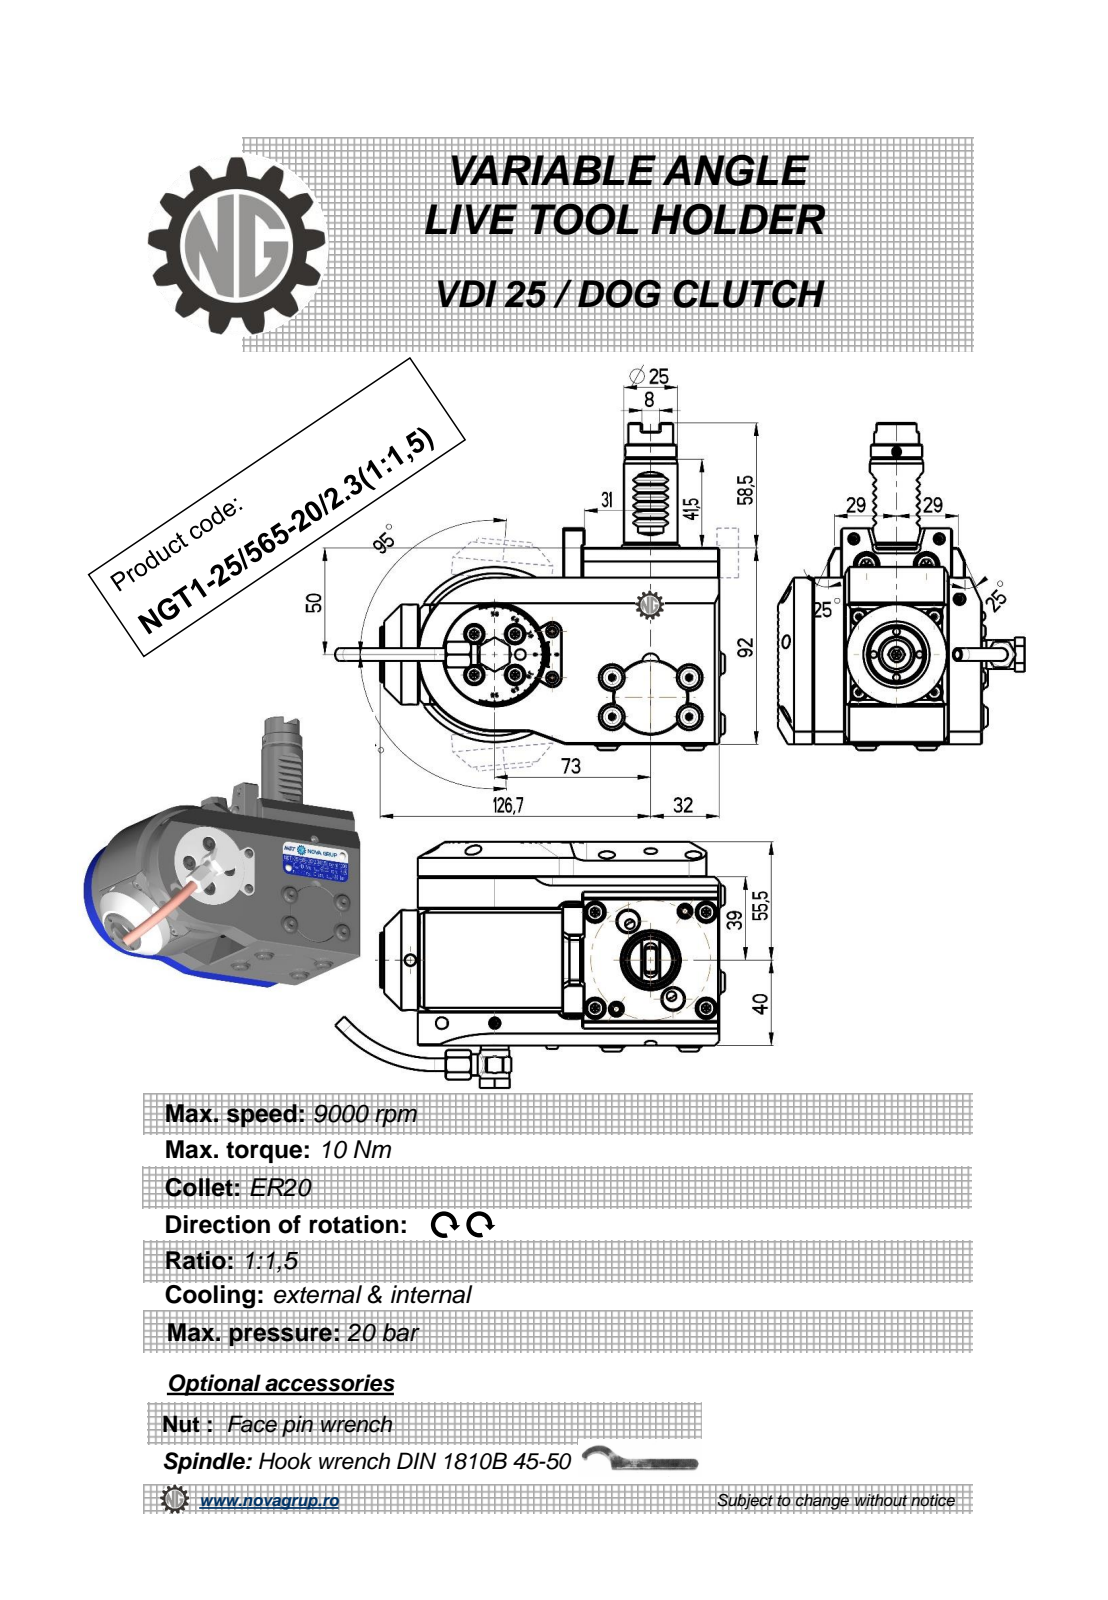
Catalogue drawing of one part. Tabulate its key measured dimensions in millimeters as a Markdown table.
| quantity | value |
| --- | --- |
| part name | NGT1_25_565_20_2_3_1_1_5 |
| STEP written by | PRO/ENGINEER BY PARAMETRIC TECHNOLOGY CORPORATION, 2010280 (CONFIG_CONTROL_DESIGN) |
| units | millimeters |
| bodies | 1 solid, 971 faces (488 planar, 267 cylindrical, 216 other) |
| overall size | 182.42 × 153.25 × 115.4 |
| volume | 1 033 000 mm³ |
| surface area | 86 039 mm² |
| round holes (diameter × count) | 3.2 × 4, 4 × 3, 4.2 × 2, 5 × 2, 3 × 1, 6 × 1, 6.2 × 1, 9 × 1, 11 × 1, 16 × 1 |
| round bosses / shafts (diameter × count) | 11.8 × 12, 9.5 × 12, 10 × 2, 5.7 × 2, 47 × 1, 34 × 1, 26 × 1, 25 × 1 |
| partial cylindrical surfaces (radius × count) | 0.24 × 60, 0.3 × 12, 0.26 × 10, 8 × 7, 0.2 × 6, 0.5 × 6, 1 × 2, 6 × 2 |
| main face-to-face distances | 92, 95.5, 16.5, 56.5, 16, 64, 6, 14, 8, 83.7 |
| hole center spacings | 10.75, 15.2, 21.5, 46.93, 50.17, 50.56, 54, 56.84 |
